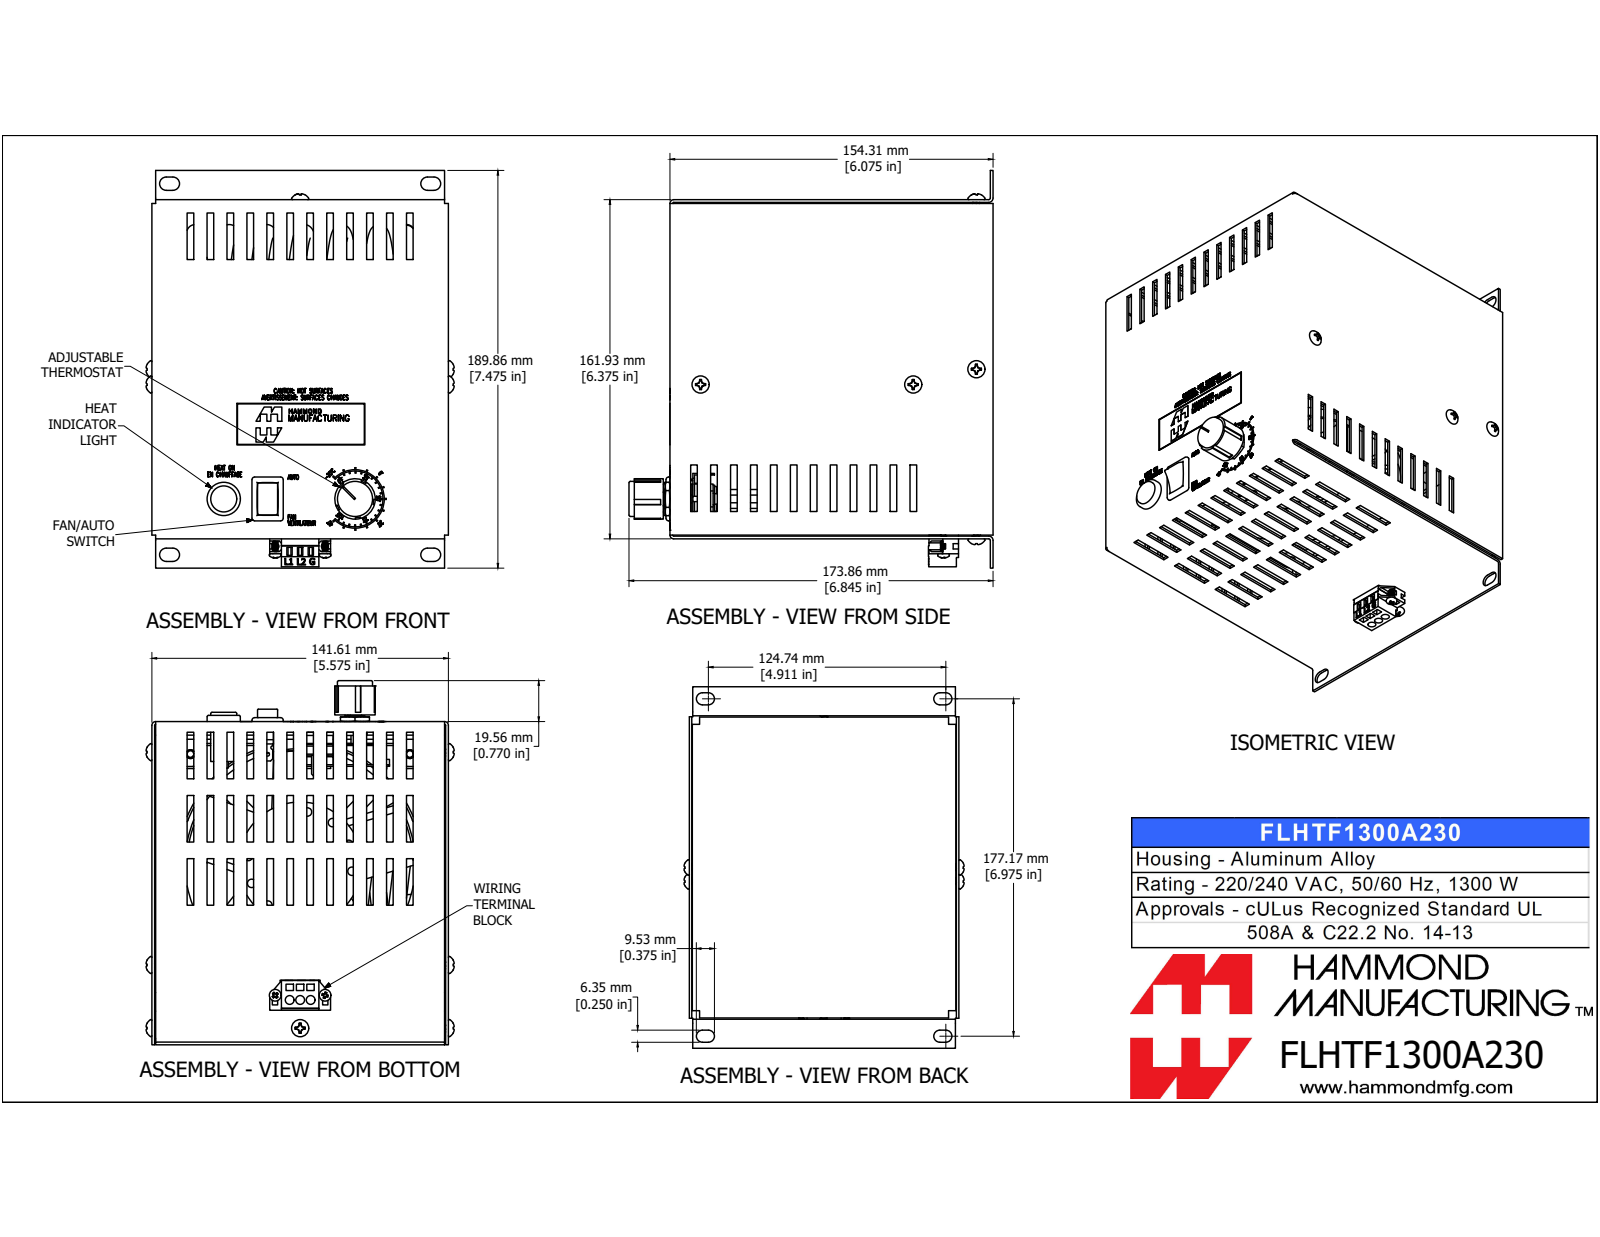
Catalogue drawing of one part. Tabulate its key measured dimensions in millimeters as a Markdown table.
| quantity | value |
| --- | --- |
| part name | FLHTF1300A230 |
| STEP written by | SolidWorks 2019 (AUTOMOTIVE_DESIGN) |
| units | millimeters |
| bodies | 17 solids, 4329 faces (3818 planar, 266 cylindrical, 245 other) |
| overall size | 189.9 × 173.9 × 147.1 |
| volume | 266 500 mm³ |
| surface area | 331 000 mm² |
| round holes (diameter × count) | 3.5 × 4, 4.6 × 4, 5.2 × 4, 4.2 × 3, 2.2 × 2, 3 × 2, 3.3 × 2, 4.8 × 2, 1.7 × 1, 1.8 × 1, 6.4 × 1, 9.7 × 1 |
| round bosses / shafts (diameter × count) | 4.2 × 4, 2.6 × 4, 4.3 × 2, 2.7 × 2, 19.3 × 1, 16.8 × 1, 16.5 × 1, 15.9 × 1 |
| partial cylindrical surfaces (radius × count) | 3.2 × 38, 1.3 × 17, 16 × 12, 3.8 × 9, 0.6 × 8, 0.5 × 4, 1.8 × 4, 0.4 × 2 |
| main face-to-face distances | 1.3, 140.3, 2.5, 160.6, 1.3, 141.6, 139, 152.8, 154.1, 150.3 |
| hole center spacings | 5, 7.3, 12.1, 14.4, 14.4, 17.1, 19.7, 19.7 |
